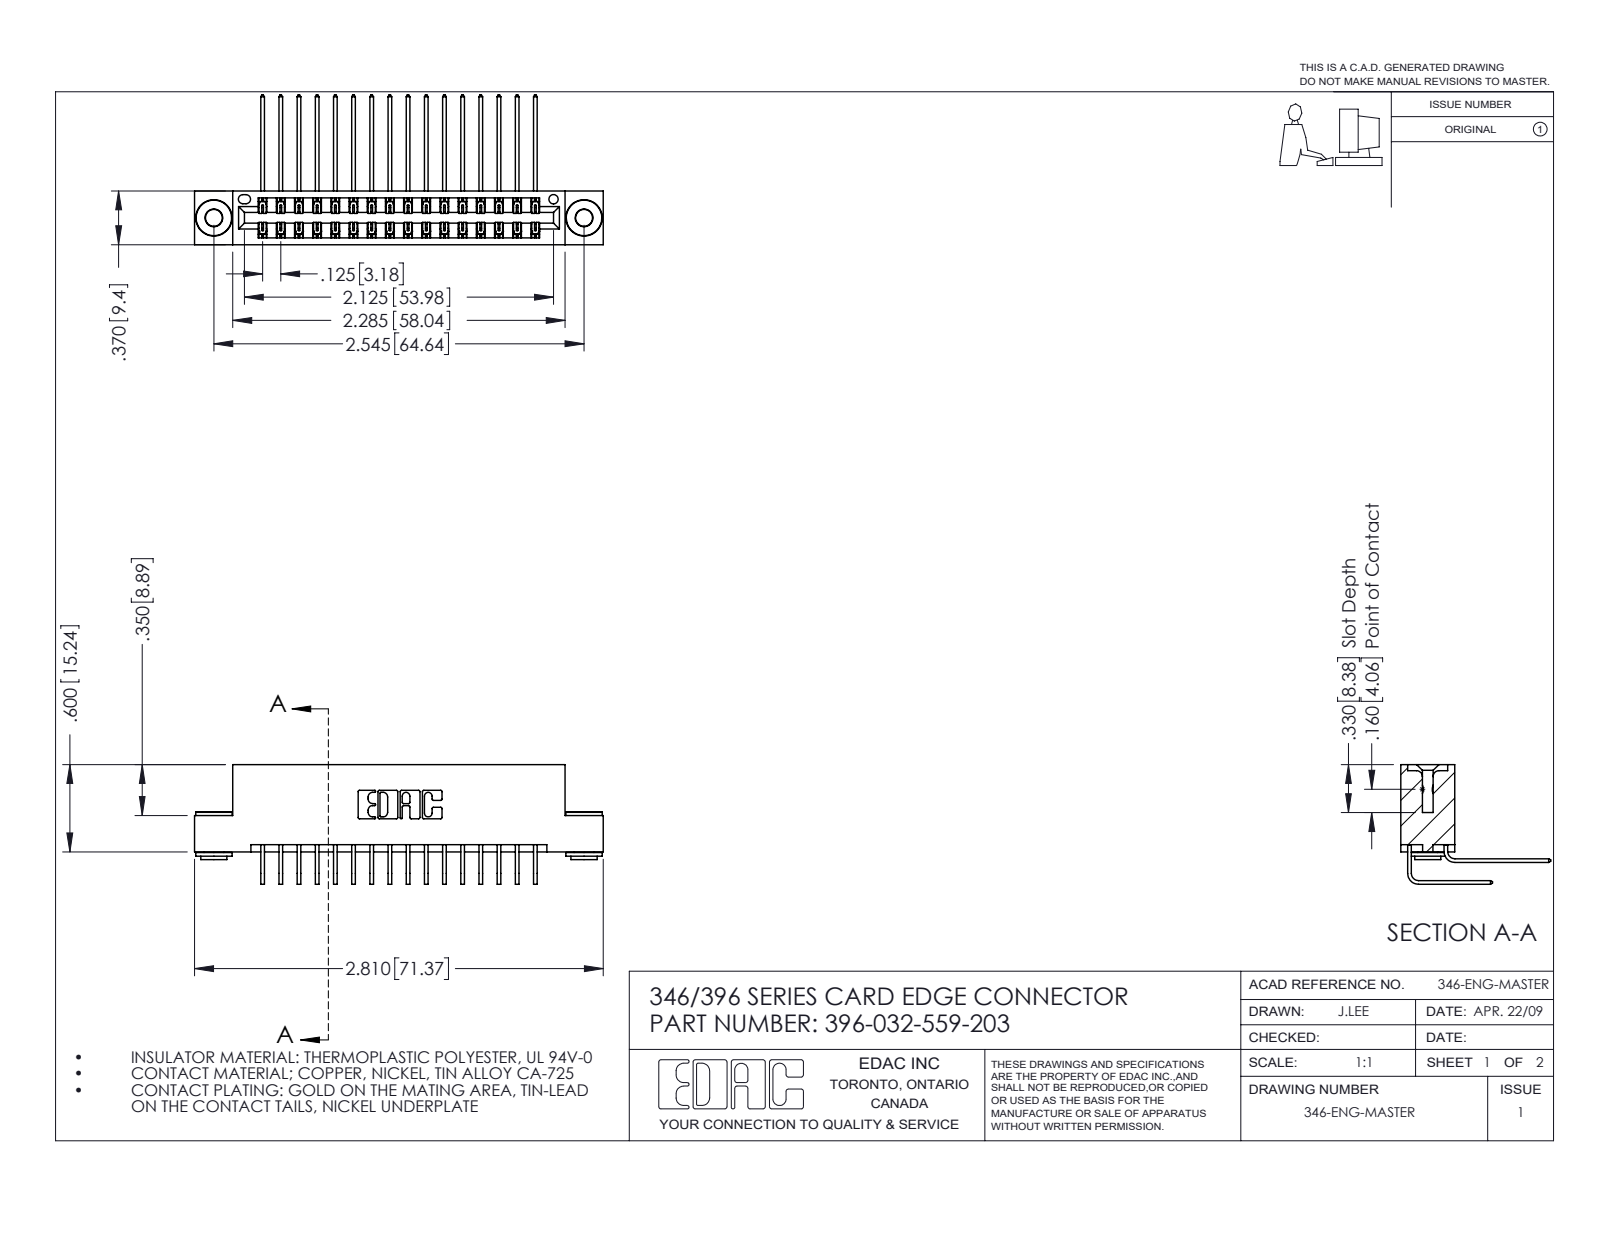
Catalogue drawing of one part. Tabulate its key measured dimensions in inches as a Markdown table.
| quantity | value |
| --- | --- |
| part name | 396-032-559-203; 345-292-001_558 559 Tail - 1; 345-250-002_345-250-002-102; 345-292-001_559 Tail - 2 (+1 more) |
| STEP written by | SolidWorks 2016 (CONFIG_CONTROL_DESIGN) |
| units | inches |
| bodies | 35 solids, 1888 faces (1270 planar, 610 cylindrical, 8 other) |
| overall size | 2.81 × 1.03 × 0.823 |
| volume | 0.425 in³ |
| surface area | 15.9 in² |
| round holes (diameter × count) | 0.116 × 2, 0.156 × 2, 0.064 × 1 |
| round bosses / shafts (diameter × count) | 0.25 × 2, 0.18 × 2, 0.136 × 2 |
| partial cylindrical surfaces (radius × count) | 0.006 × 48, 0.01 × 22, 0.007 × 6, 0.031 × 6, 0.026 × 3, 0.014 × 2, 0.022 × 2, 0.024 × 2 |
| main face-to-face distances | 0.048, 0.322, 0.25, 0.025, 0.37, 0.072, 0.298, 0.275, 0.148, 0.222 |
| hole center spacings | 0.246, 2.338, 2.545 |
